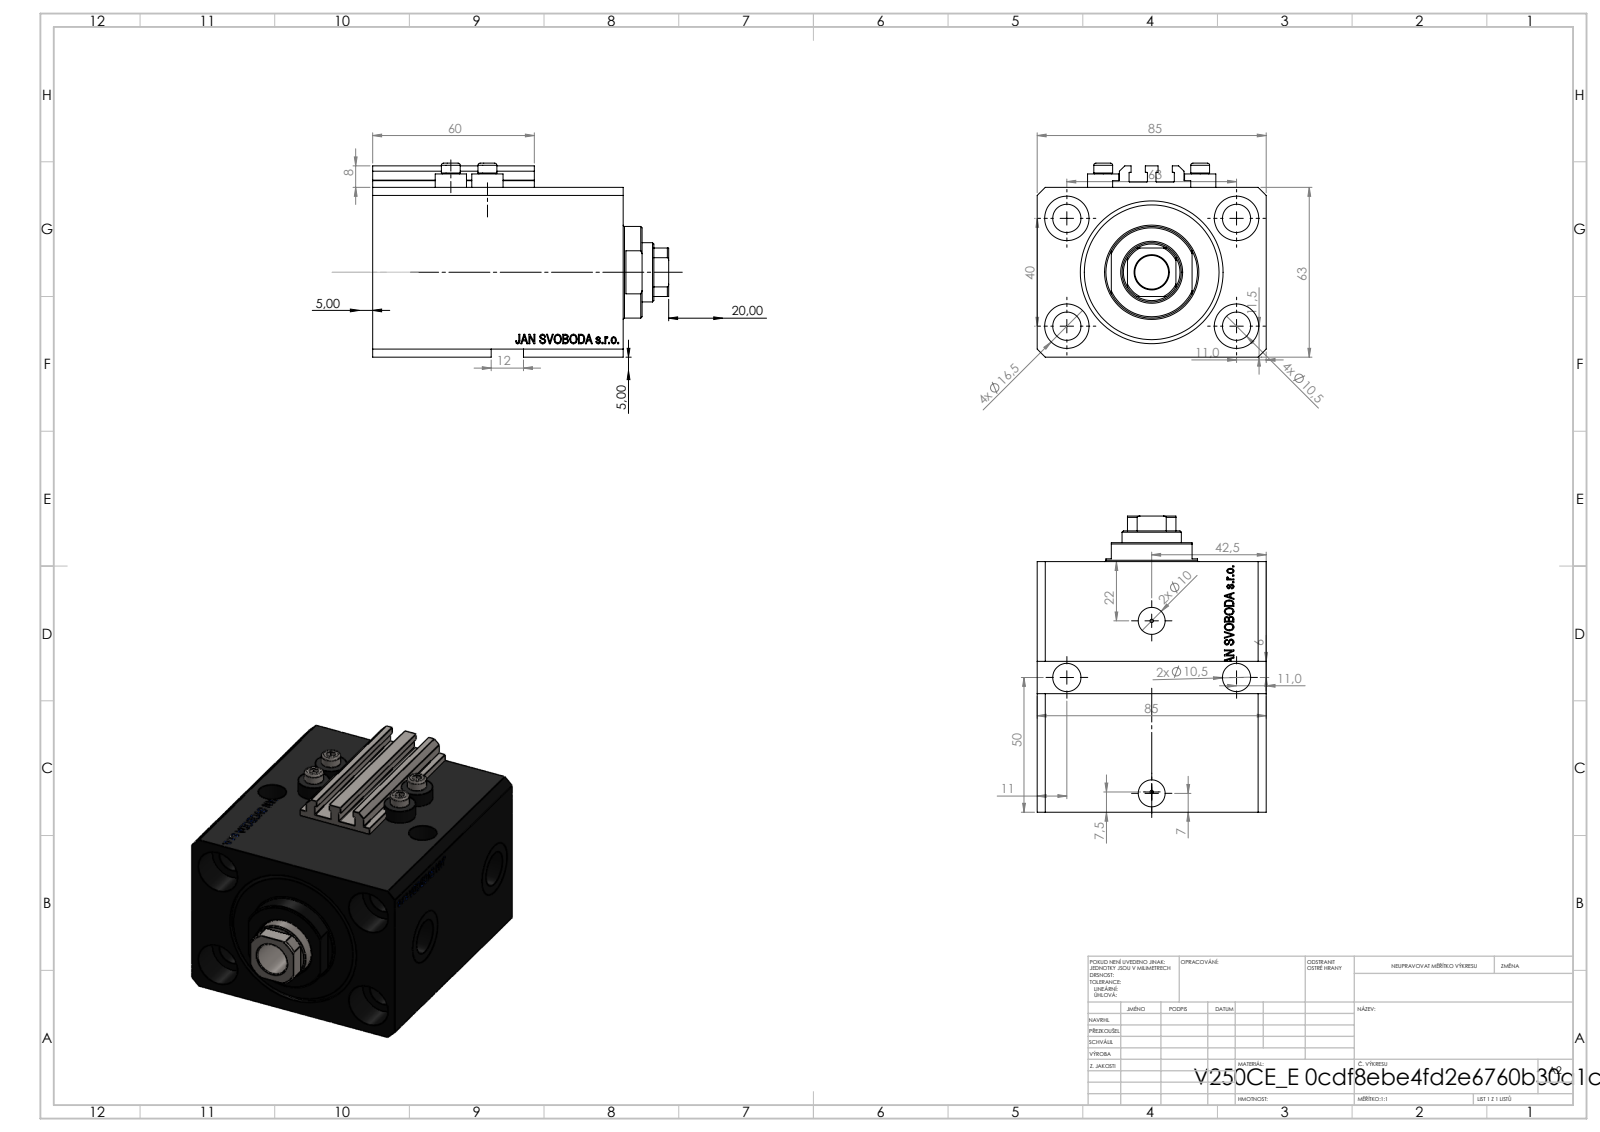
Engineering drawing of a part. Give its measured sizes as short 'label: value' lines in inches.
name: V250CE_C_VCP; V250CE_VC_E; V250CE_E_Body; ALLEN BOLT V250CE
written by: SolidWorks 2019 (CONFIG_CONTROL_DESIGN)
unit: in
bodies: 8 solids, 1087 faces (535 planar, 126 cylindrical, 426 other)
size: 4.327 × 3.346 × 2.835
volume: 26.68 in³; area: 151.8 in²
holes: 6× ⌀0.413, 4× ⌀0.049, 4× ⌀0.157, 4× ⌀0.65, 2× ⌀0.394, 2× ⌀0.518, 2× ⌀0.787, 1× ⌀0.492, 1× ⌀0.866, 1× ⌀1.575, 1× ⌀2.087
bosses: 4× ⌀0.457, 4× ⌀0.276, 1× ⌀1.339
rounds: 10× R0.008, 1× R0.413
face distances: 2.48, 3.346, 3.661, 2.594, 2.146, 1.067, 0.449, 3.213, 0.118, 2.559
hole spacings: 1.469, 2.48, 0.535, 0.606, 0.983, 1.103, 1.119, 1.324
